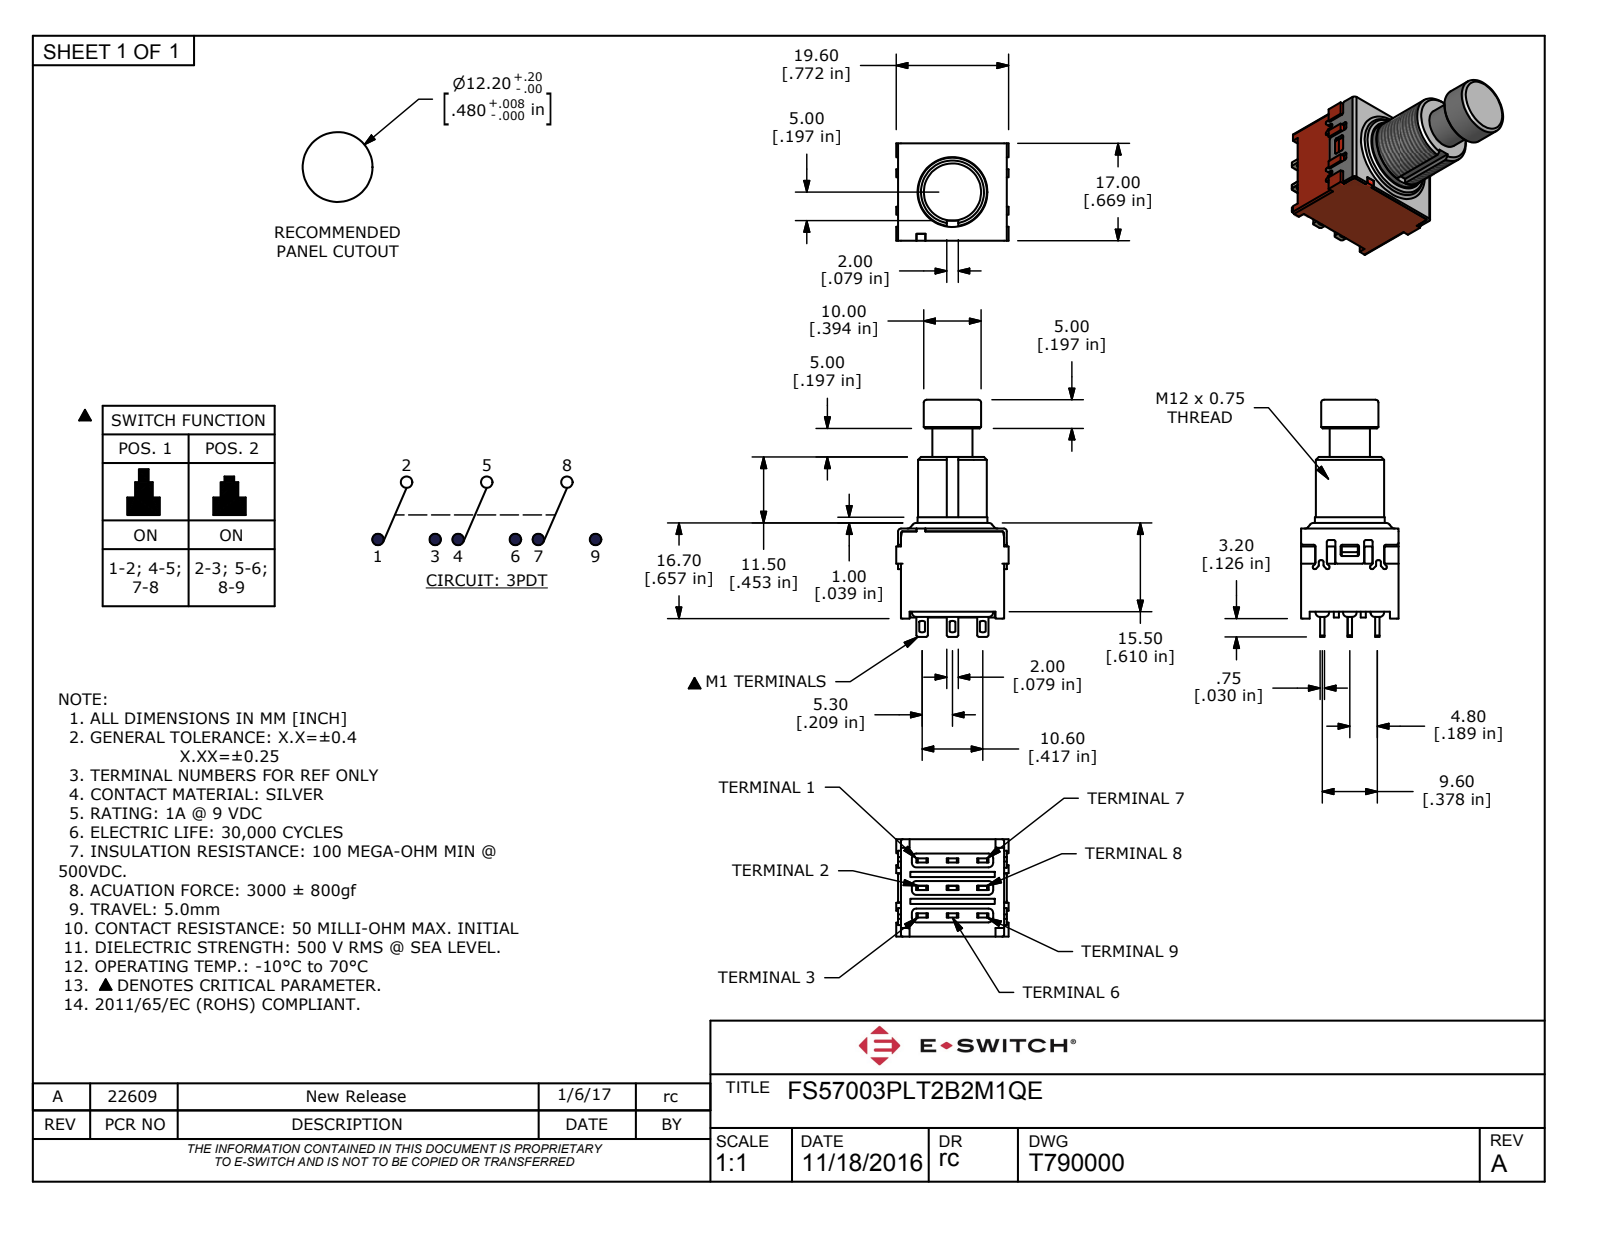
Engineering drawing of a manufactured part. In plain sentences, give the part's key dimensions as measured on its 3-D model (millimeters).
The part is named "FS57003PLT2B2M1QE". Its 3-D file was written by "Autodesk Inventor 2022 (AUTOMOTIVE_DESIGN)". It is 1 solid with 429 faces: 277 planar, 127 cylindrical and 25 other. Overall it measures 41.4 by 19.6 by 17 millimeters. Its volume is 3 125 cubic millimeters and its surface area 4 709 square millimeters. Round holes: 1 of diameter 9. Round bosses or shafts: 1 of diameter 12.2, 1 of diameter 12, 1 of diameter 10, 1 of diameter 7. Partial cylindrical surfaces (rounded edges, fillets, slot ends): 36 of radius 0.3, 20 of radius 0.8, 6 of radius 0.5, 3 of radius 1. The main face-to-face distances are 1.2, 15.8, 16.8, 17, 0.5, 15.6, 14.6, 18, 10, 1.7.
